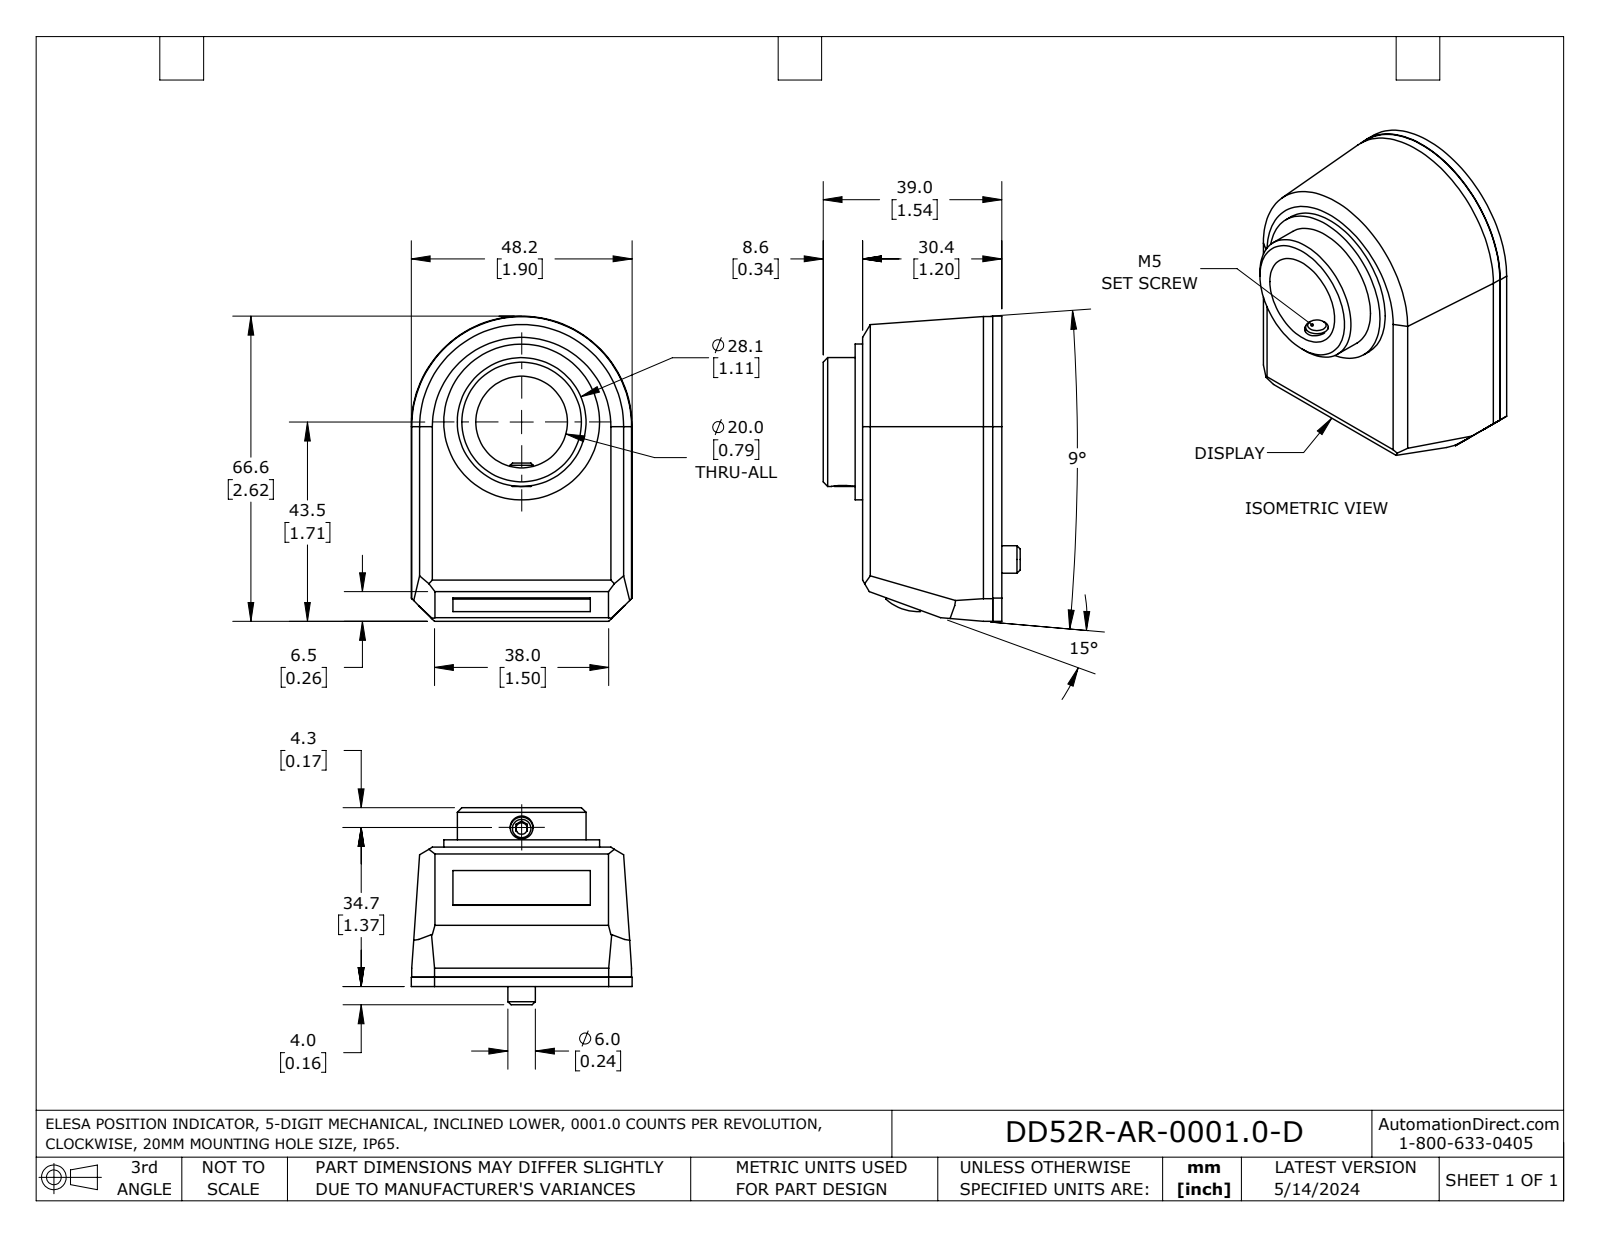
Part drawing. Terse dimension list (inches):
name: DD52R-AR-METRIC
written by: SolidWorks 2023 (AUTOMOTIVE_DESIGN)
unit: in
bodies: 4 solids, 66 faces (45 planar, 13 cylindrical, 8 other)
size: 2.622 × 1.898 × 1.693
volume: 4.372 in³; area: 34.72 in²
holes: 1× ⌀0.197, 1× ⌀0.787, 1× ⌀1.106, 1× ⌀1.575
bosses: 1× ⌀1.339, 1× ⌀0.236, 1× ⌀0.197
rounds: 1× R0.049, 1× R0.409, 1× R0.945, 1× R0.949
face distances: 0.079, 1.118, 1.197, 0.157, 1.039, 1.181, 0.063, 1.102, 1.26, 1.535
